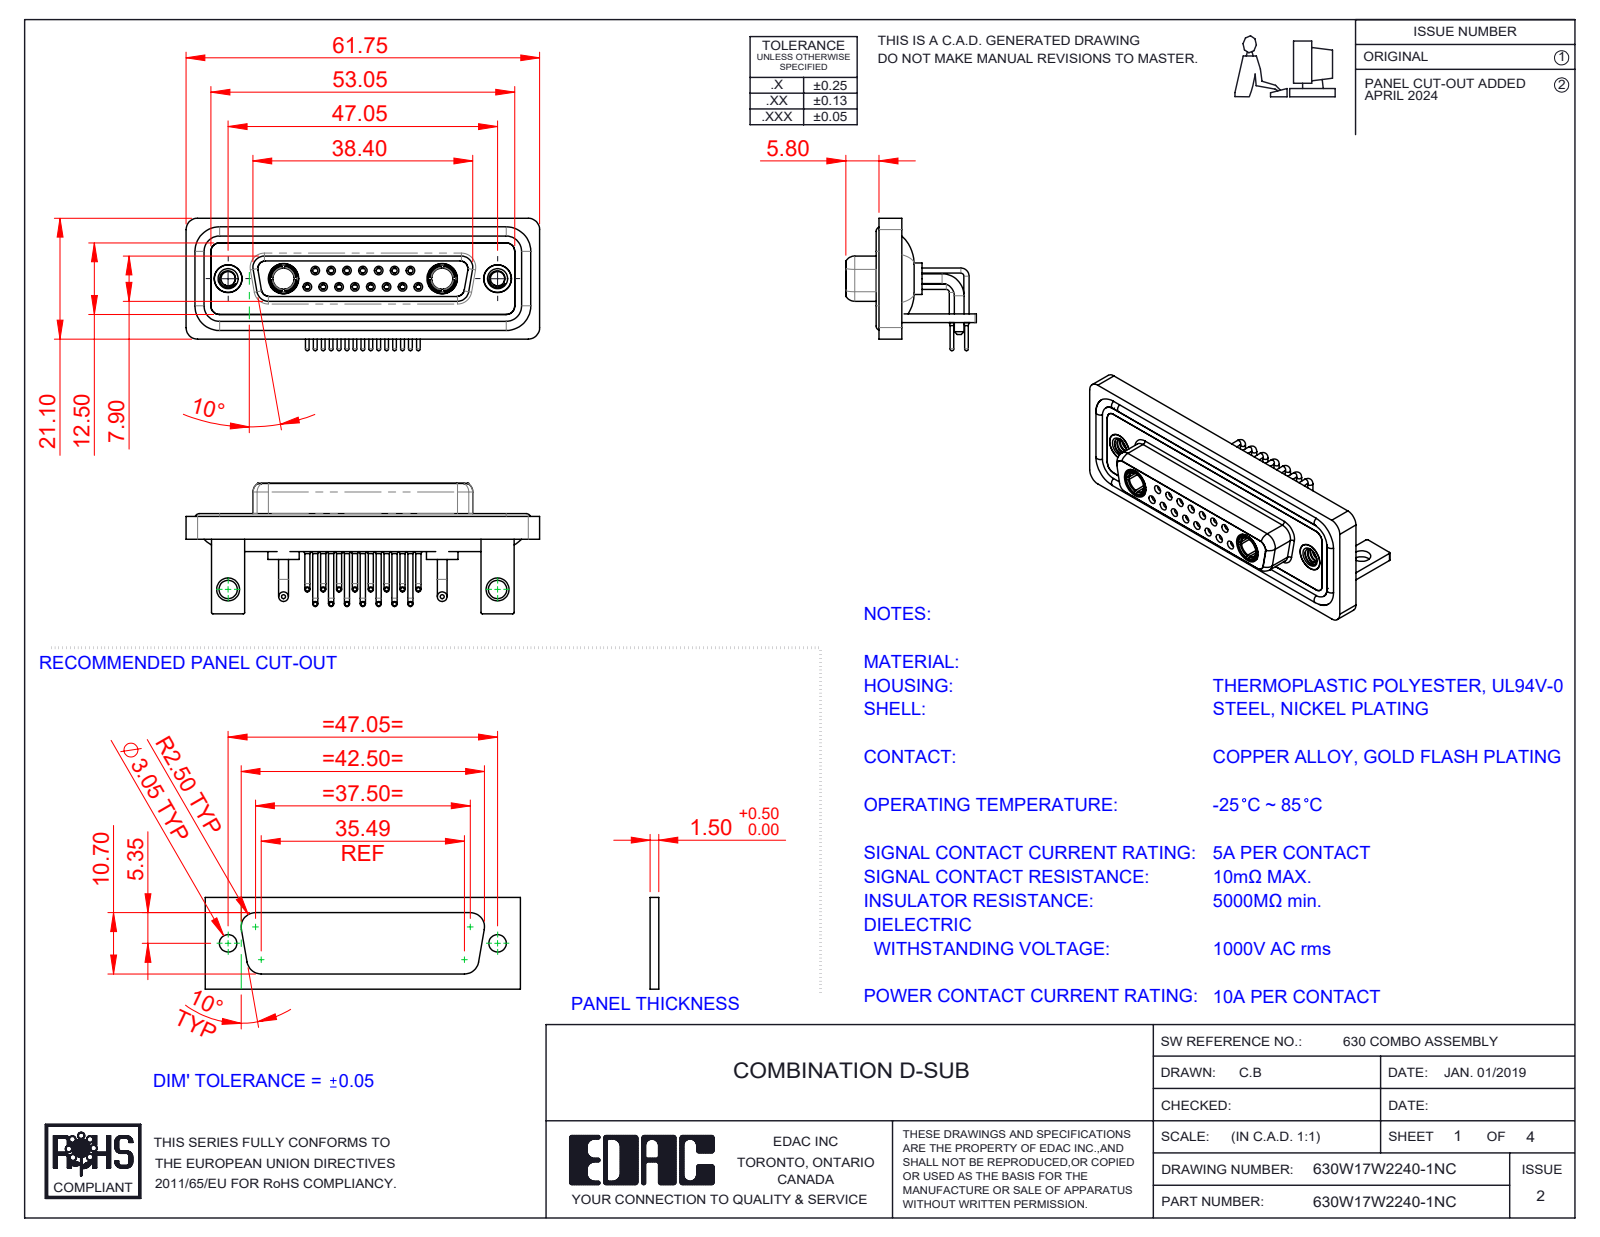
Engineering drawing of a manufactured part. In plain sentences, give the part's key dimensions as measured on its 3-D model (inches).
The part is named "630Combo Threaded Rivet_A; 630Combo Waterproof Housing_25 Contacts; Power Socket_10A RA; 630W17W2240-1NC (+6 more)". Its 3-D file was written by "SolidWorks 2023 (CONFIG_CONTROL_DESIGN)". It is 28 solids with 1379 faces: 408 planar, 605 cylindrical and 366 other. Overall it measures 2.431 by 0.91 by 0.898 inches. Its volume is 0.533 cubic inches and its surface area 23.51 square inches. Round holes: 15 of diameter 0.035, 15 of diameter 0.043, 15 of diameter 0.059, 15 of diameter 0.079, 8 of diameter 0.063, 7 of diameter 0.067, 4 of diameter 0.191, 2 of diameter 0.098, 2 of diameter 0.126, 2 of diameter 0.146, 2 of diameter 0.157, 2 of diameter 0.159. Round bosses or shafts: 15 of diameter 0.035, 15 of diameter 0.026, 11 of diameter 0.063, 4 of diameter 0.067, 2 of diameter 0.217, 2 of diameter 0.205, 2 of diameter 0.195, 2 of diameter 0.195. Partial cylindrical surfaces (rounded edges, fillets, slot ends): 19 of radius 0.079, 18 of radius 0.059, 16 of radius 0.01, 8 of radius 0.053, 8 of radius 0.063, 5 of radius 0.02, 4 of radius 0.024, 4 of radius 0.026. The main face-to-face distances are 0.016, 0.071, 0.114, 0.146, 0.059, 0.161, 0.043, 0.055, 0.063, 0.122. The hole center spacings are 0.124, 0.109, 0.218, 0.327, 0.198, 0.295, 0.436, 0.198.
